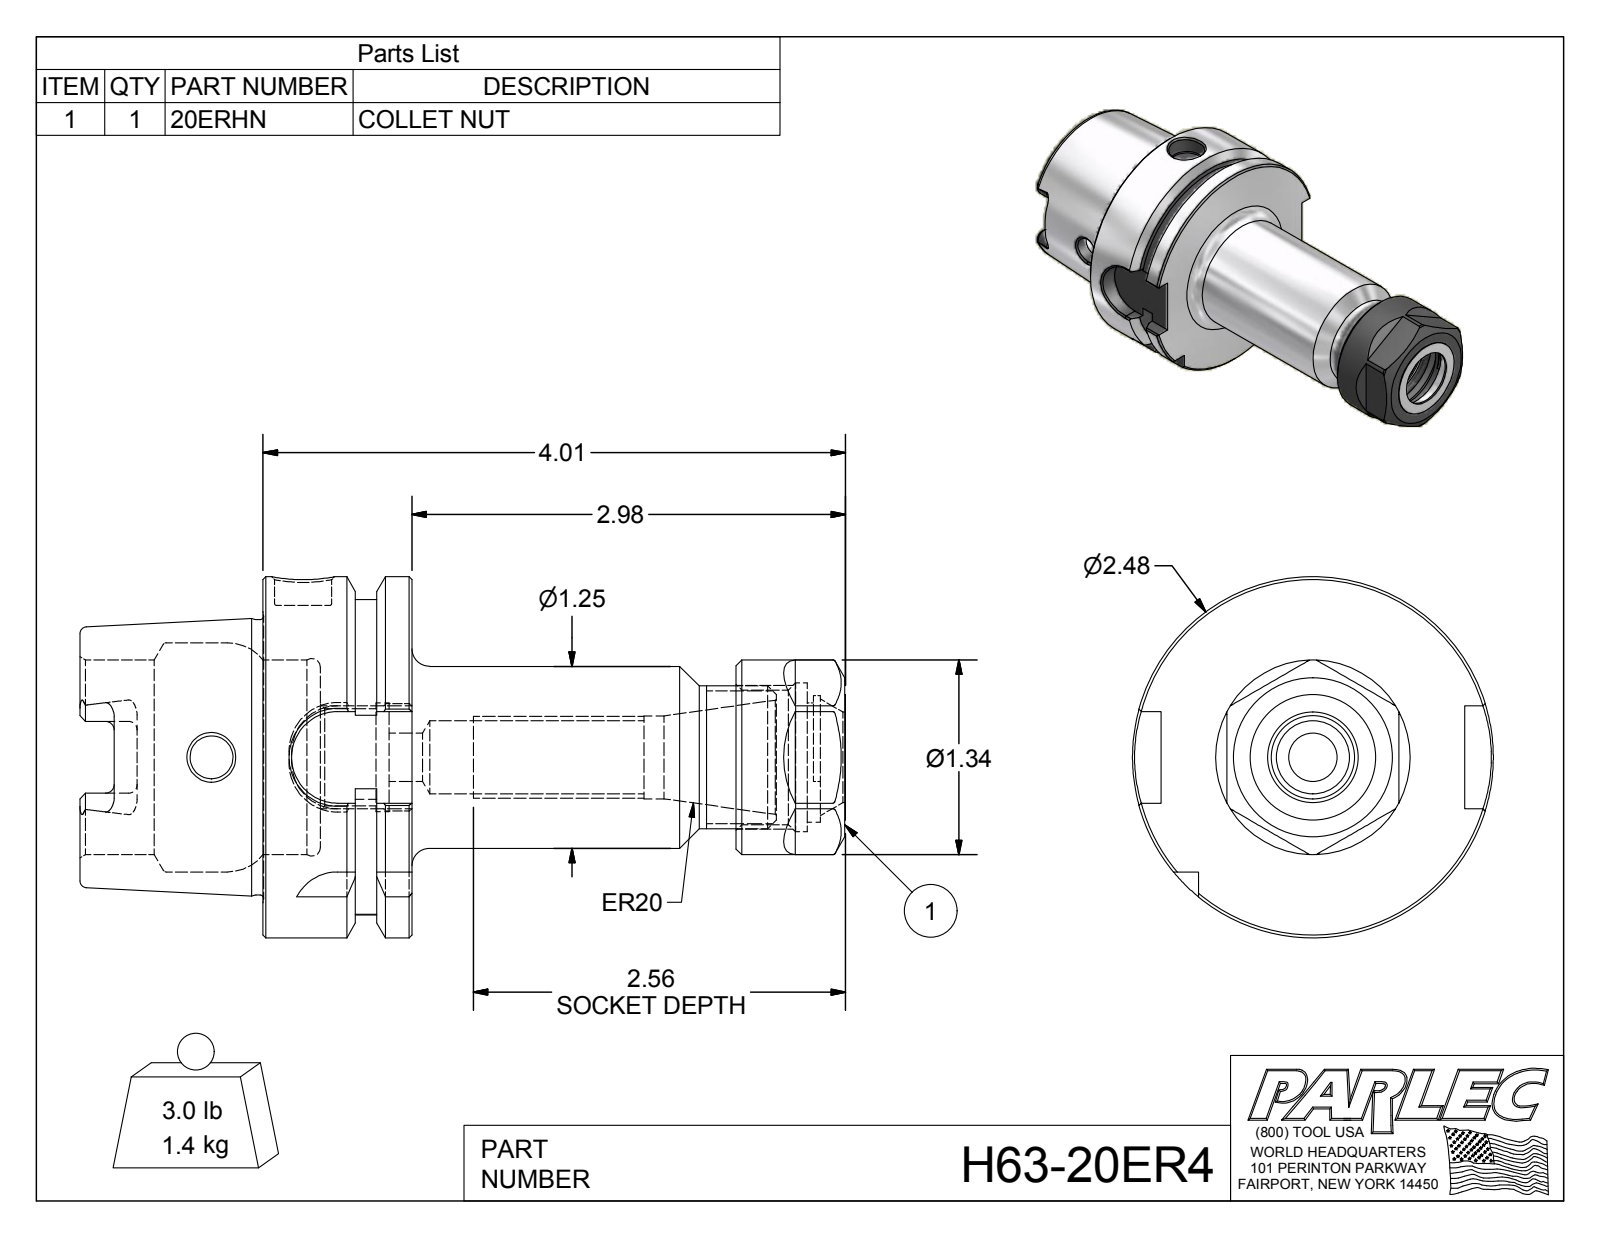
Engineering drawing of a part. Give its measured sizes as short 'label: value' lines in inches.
name: H63-20ER4; H63-20ER4-1; 20ERHN
written by: Autodesk Inventor 2012 (AUTOMOTIVE_DESIGN)
unit: in
bodies: 2 solids, 174 faces (70 planar, 43 cylindrical, 61 other)
size: 5.265 × 2.48 × 2.48
volume: 7.634 in³; area: 54.87 in²
holes: 1× ⌀0.295, 1× ⌀0.335, 1× ⌀0.394, 1× ⌀0.502, 1× ⌀0.57, 1× ⌀0.62, 1× ⌀0.666, 1× ⌀0.749, 1× ⌀0.82, 1× ⌀0.925, 1× ⌀1.024, 1× ⌀1.339
bosses: 1× ⌀2.48, 1× ⌀1.891, 1× ⌀1.25, 1× ⌀0.984, 1× ⌀0.86
rounds: 6× R0.059, 4× R0.113, 4× R0.315, 1× R0.423, 1× R1.083
face distances: 1.024, 0.241, 0.389, 0.394, 0.63, 1.26, 1.654, 2.283, 1.181, 2.043
hole spacings: 0.037
